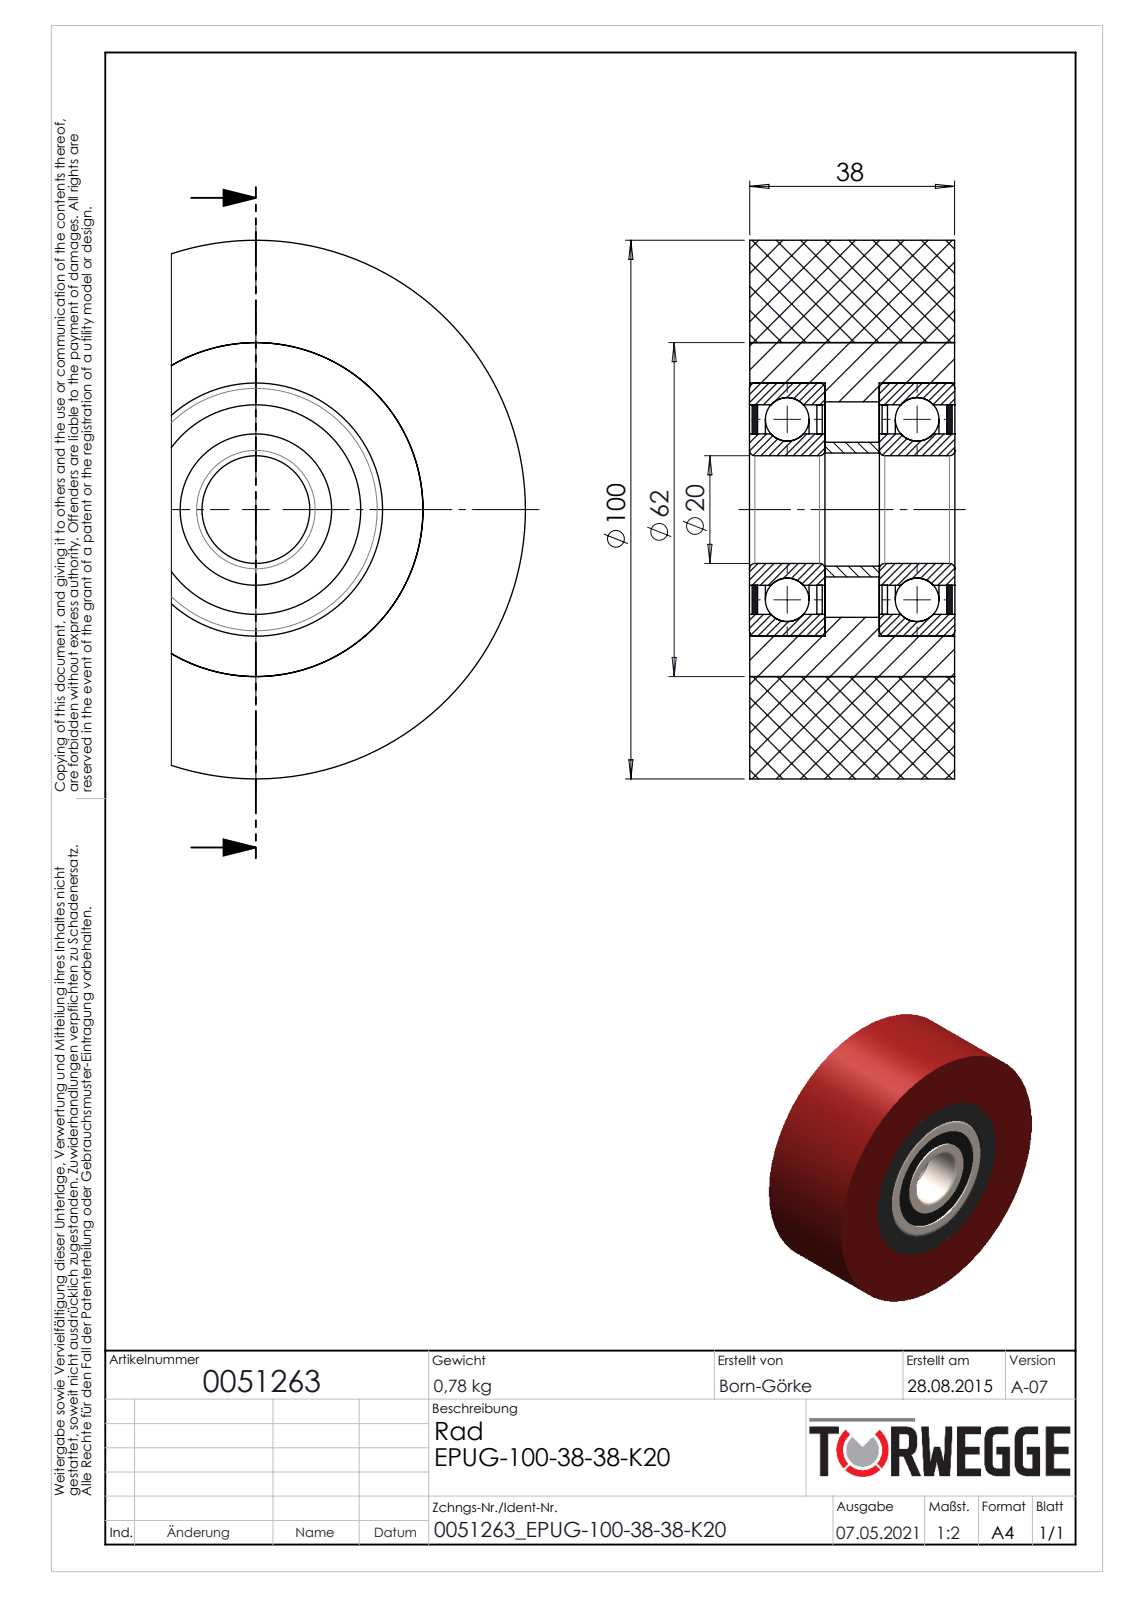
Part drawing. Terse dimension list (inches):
name: 0051263
written by: SolidWorks 2020 (AUTOMOTIVE_DESIGN)
unit: in
bodies: 13 solids, 116 faces (24 planar, 56 cylindrical, 36 other)
size: 3.937 × 3.937 × 1.496
volume: 16.68 in³; area: 113.1 in²
holes: 1× ⌀0.787, 1× ⌀0.827, 1× ⌀1.106, 1× ⌀1.531, 1× ⌀1.575, 1× ⌀1.85, 1× ⌀2.441
bosses: 1× ⌀3.937, 1× ⌀0.984
face distances: 1.496, 0.945, 0.472, 0.02, 0.059, 0.492, 0.531, 0.039, 0.551, 0.512
